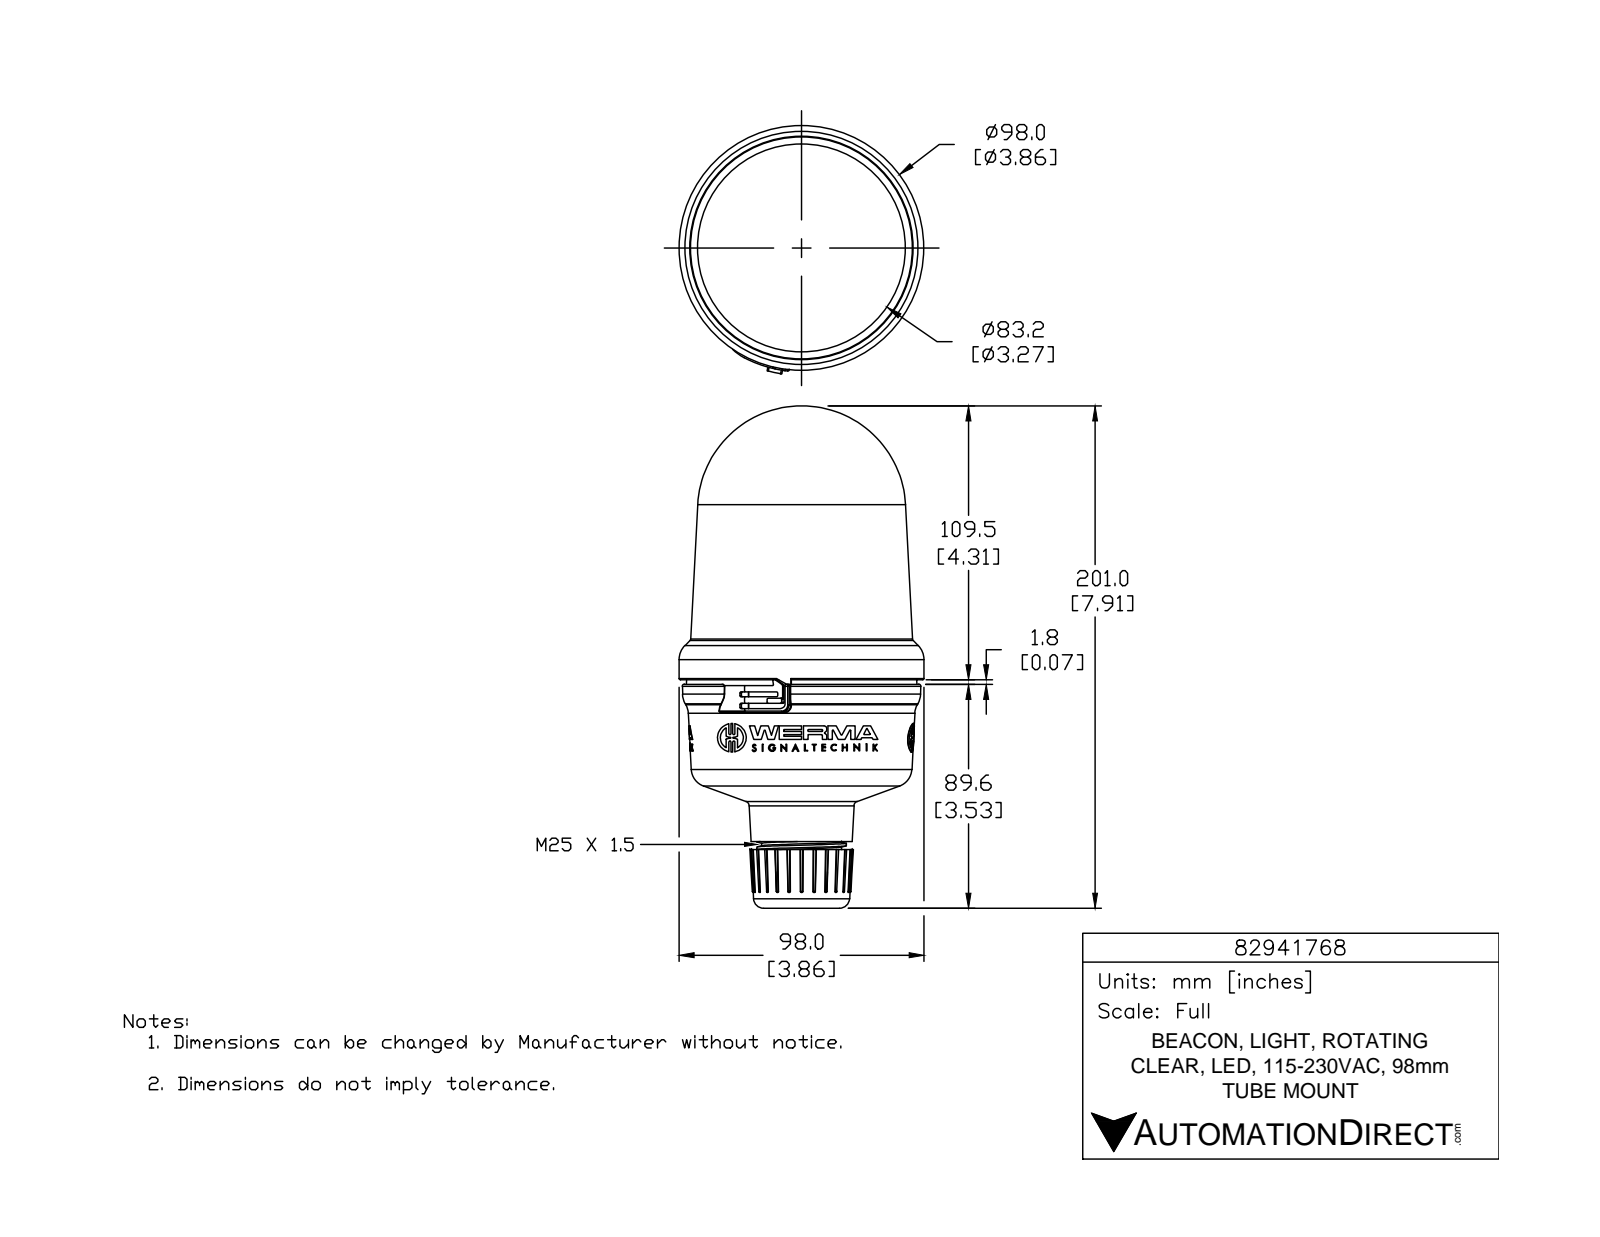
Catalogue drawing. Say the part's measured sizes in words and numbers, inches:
The part is named "82941768". Its 3-D file was written by "SolidWorks 2015 (AUTOMOTIVE_DESIGN)". It is 1 solid with 1006 faces: 554 planar, 189 cylindrical and 263 other. Overall it measures 7.914 by 3.912 by 3.858 inches. Its volume is 54.7 cubic inches and its surface area 91.39 square inches. Round holes: 3 of diameter 0.078, 1 of diameter 1.013, 1 of diameter 1.024. Round bosses or shafts: 3 of diameter 0.452, 3 of diameter 0.113, 1 of diameter 3.858, 1 of diameter 1.409, 1 of diameter 1.261. Partial cylindrical surfaces (rounded edges, fillets, slot ends): 12 of radius 0.02, 9 of radius 0.007, 6 of radius 0.007, 6 of radius 0.016, 6 of radius 0.016, 6 of radius 0.016, 6 of radius 0.262, 3 of radius 0.006. The main face-to-face distances are 2.214, 0.462, 2.676, 0.335, 0.127, 2.548, 2.603, 2.476, 2.141, 0.073.
